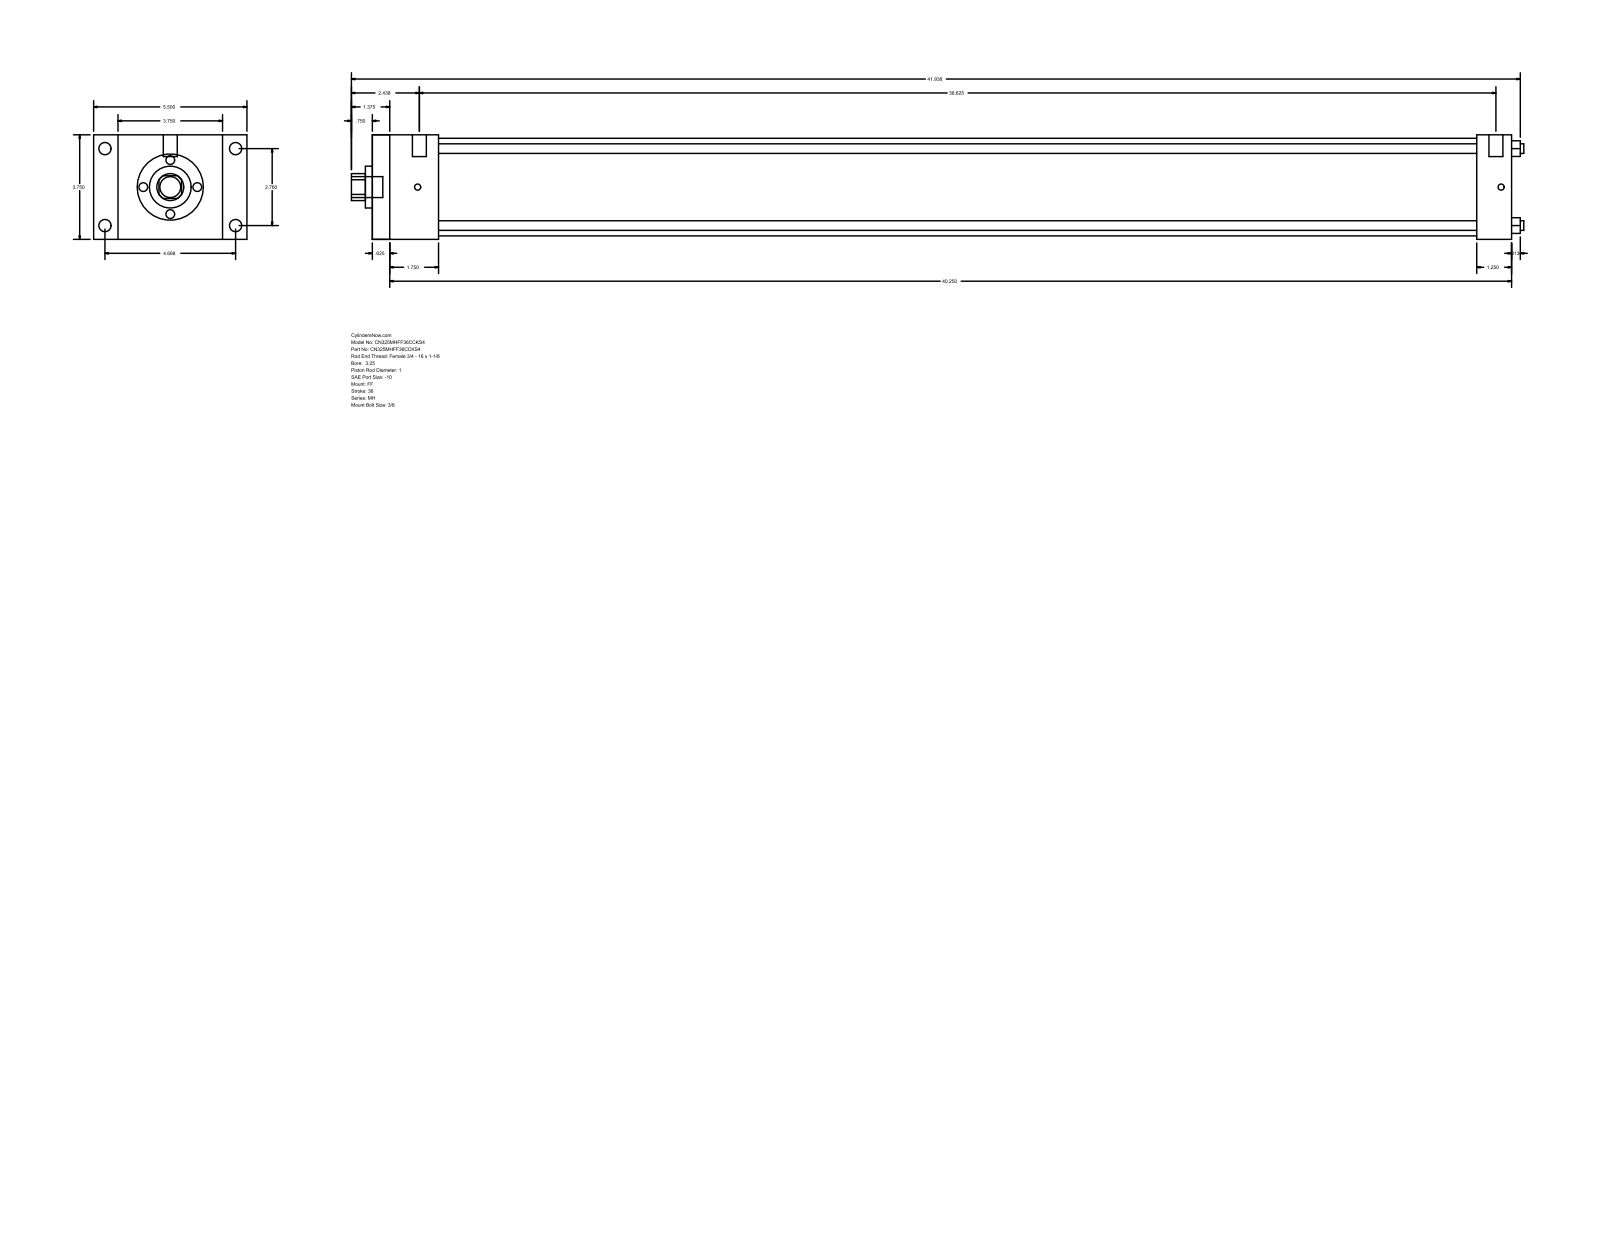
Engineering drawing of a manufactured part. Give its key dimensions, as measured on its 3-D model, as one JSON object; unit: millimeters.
{"part_name": "MH_FF__0325_1", "step_written_by": "GSSL Pune (CONFIG_CONTROL_DESIGN)", "units": "millimeters", "bodies": {"solids": 0, "faces": 92, "planar": 64, "cylindrical": 28, "other": 0}, "overall_size": [1068.39, 139.7, 95.25], "round_holes": [[8.76, 4], [25.4, 1], [38.1, 1], [88.9, 1]], "round_bosses_or_shafts": [[11.13, 4], [5.56, 4], [12.7, 2], [19.05, 1]], "partial_cylinders_radius": [[12.29, 1]], "face_to_face_distances": [95.24, 1038.23, 15.87, 1022.36, 22.23, 117.47, 1006.48, 990.61, 31.75, 60.33], "hole_center_spacings": [49.57, 70.1, 99.14]}
